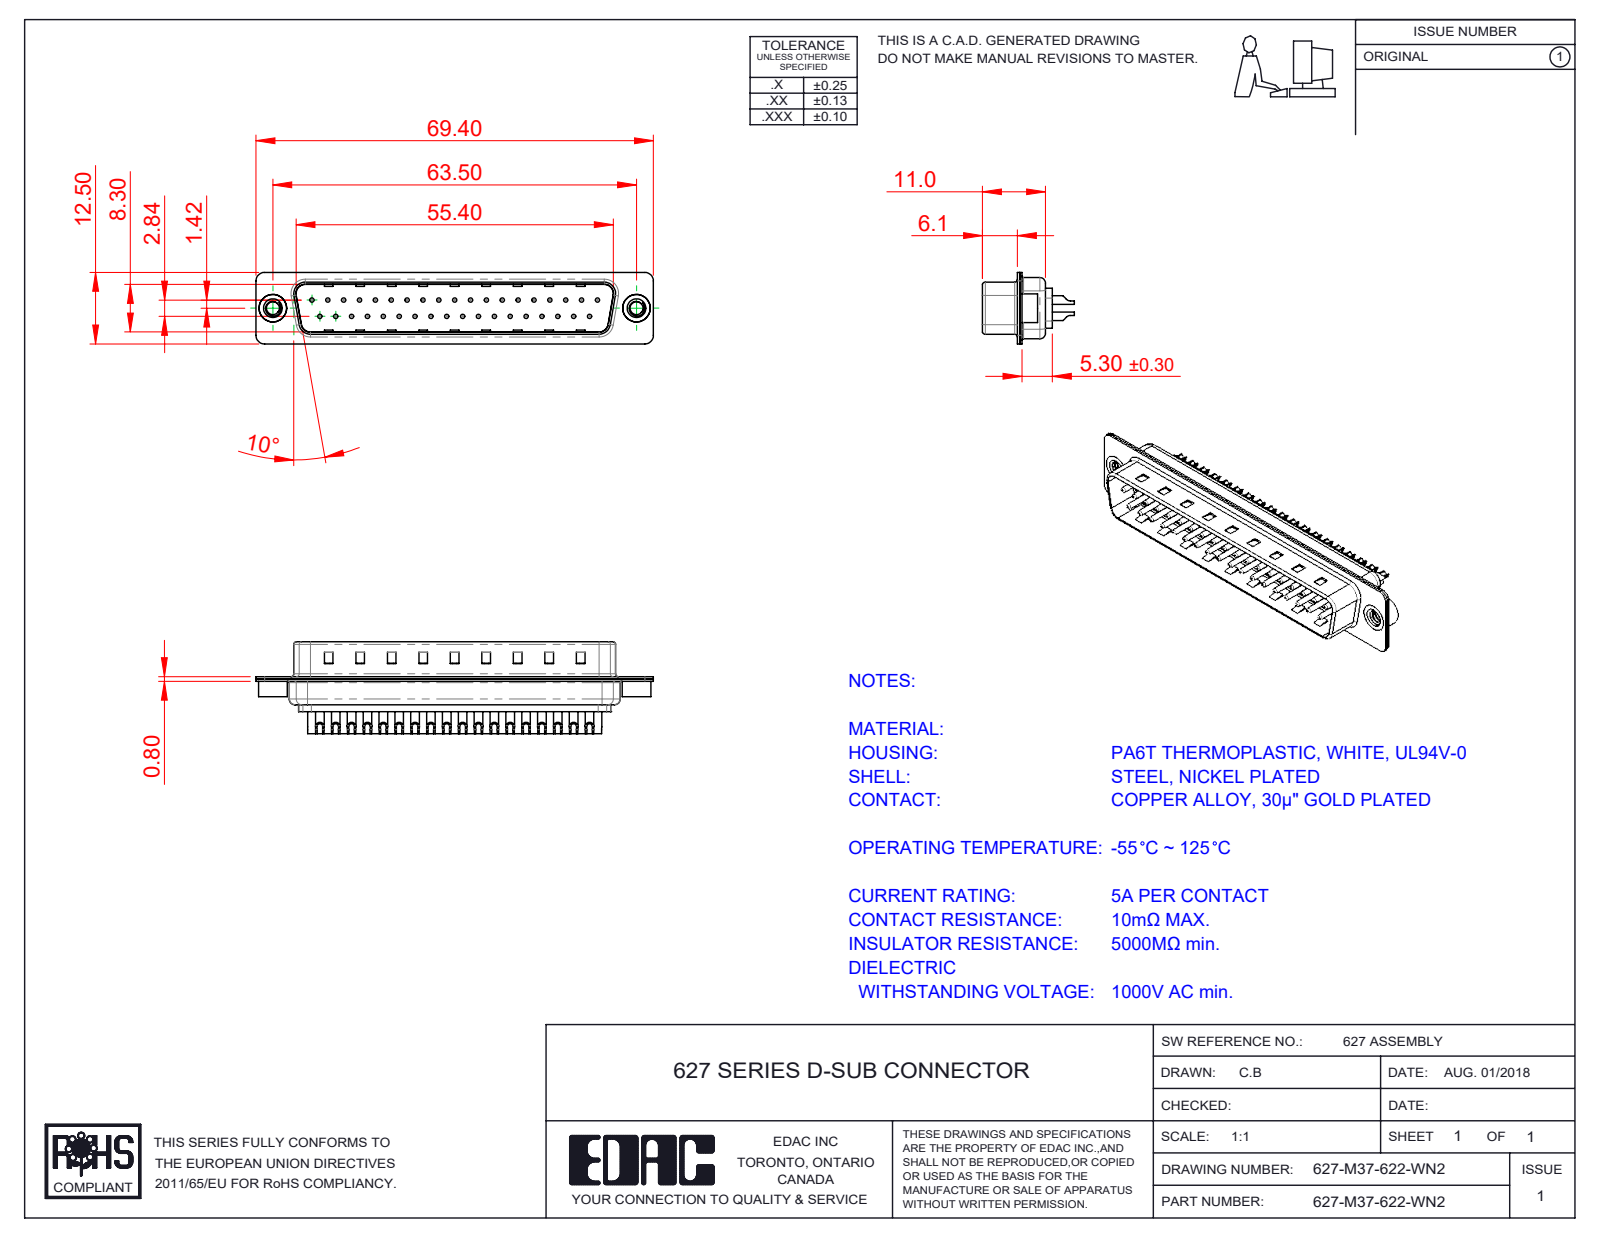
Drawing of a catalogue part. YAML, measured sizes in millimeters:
part_name: "627M Contact Row 1_22; 627M Shell Rear_37 Contacts; 627M 4-40 Threaded Rivet; 627-M37-622-WN2 (+3 more)"
step_written_by: "SolidWorks 2020 (CONFIG_CONTROL_DESIGN)"
units: millimeters
bodies: {solids: 42, faces: 1781, planar: 536, cylindrical: 733, other: 512}
overall_size: [69.4, 16.05, 12.5]
volume: 3853
surface_area: 9616
round_holes:
  - {diameter: 0.75, count: 37}
  - {diameter: 1, count: 37}
  - {diameter: 1.6, count: 37}
  - {diameter: 2, count: 37}
  - {diameter: 2.26, count: 2}
  - {diameter: 4, count: 2}
  - {diameter: 4.8, count: 2}
round_bosses_or_shafts:
  - {diameter: 1.5, count: 37}
  - {diameter: 5, count: 2}
  - {diameter: 4.9, count: 2}
partial_cylinders:
  - {radius: 1.5, count: 16}
  - {radius: 2, count: 12}
  - {radius: 0.5, count: 8}
  - {radius: 1.6, count: 8}
  - {radius: 1, count: 6}
  - {radius: 0.25, count: 4}
  - {radius: 0.6, count: 4}
  - {radius: 0.65, count: 4}
face_to_face_distances: [0.4, 0.8, 9.5, 9.1, 8.7, 9.9, 1.2, 0.75, 0.35, 5.7]
hole_center_spacings: [2.77, 5.54, 3.16, 8.31, 11.08, 13.85, 16.62, 19.39]
